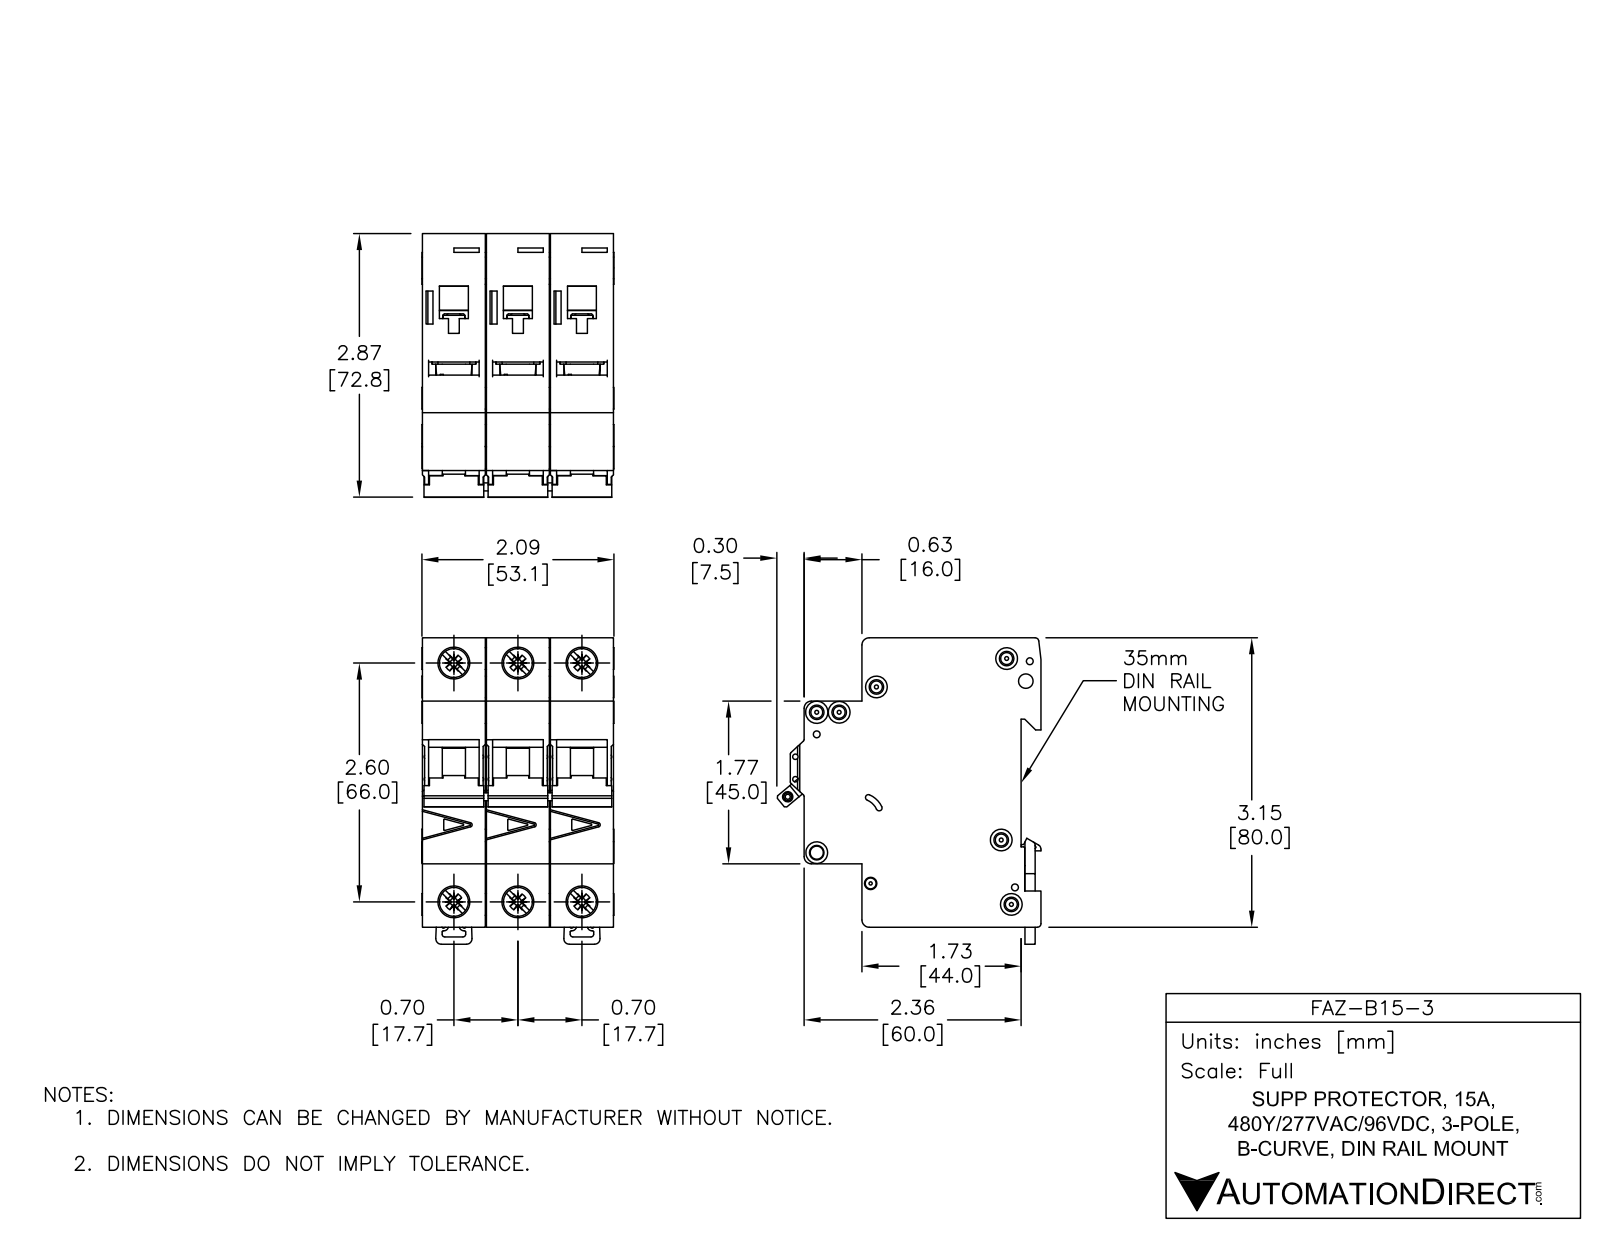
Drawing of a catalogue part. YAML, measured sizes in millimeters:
part_name: "FAZ-B15-3"
step_written_by: "SolidWorks 2014 (AUTOMOTIVE_DESIGN)"
units: millimeters
bodies: {solids: 11, faces: 1650, planar: 697, cylindrical: 590, other: 363}
overall_size: [84.78, 73.04, 53.1]
volume: 224680
surface_area: 58052
round_holes:
  - {diameter: 3.6, count: 6}
  - {diameter: 8.2, count: 4}
  - {diameter: 1.9, count: 3}
  - {diameter: 1.09, count: 2}
  - {diameter: 1.5, count: 2}
  - {diameter: 4, count: 2}
  - {diameter: 7.15, count: 2}
  - {diameter: 2.15, count: 1}
  - {diameter: 2.2, count: 1}
  - {diameter: 2.55, count: 1}
  - {diameter: 3.3, count: 1}
  - {diameter: 3.4, count: 1}
round_bosses_or_shafts:
  - {diameter: 6, count: 4}
  - {diameter: 2.5, count: 3}
  - {diameter: 8.2, count: 2}
partial_cylinders:
  - {radius: 0.25, count: 68}
  - {radius: 0.5, count: 25}
  - {radius: 1, count: 12}
  - {radius: 2, count: 12}
  - {radius: 0.2, count: 11}
  - {radius: 1.8, count: 3}
  - {radius: 0.8, count: 2}
  - {radius: 3, count: 2}
face_to_face_distances: [17.7, 17.5, 35.4, 35.2, 52.9, 17.9, 79.48, 5.5, 49.5, 44]
hole_center_spacings: [17.7, 68.33, 66, 6.2, 13.64, 35.4, 74.89, 4.81]
